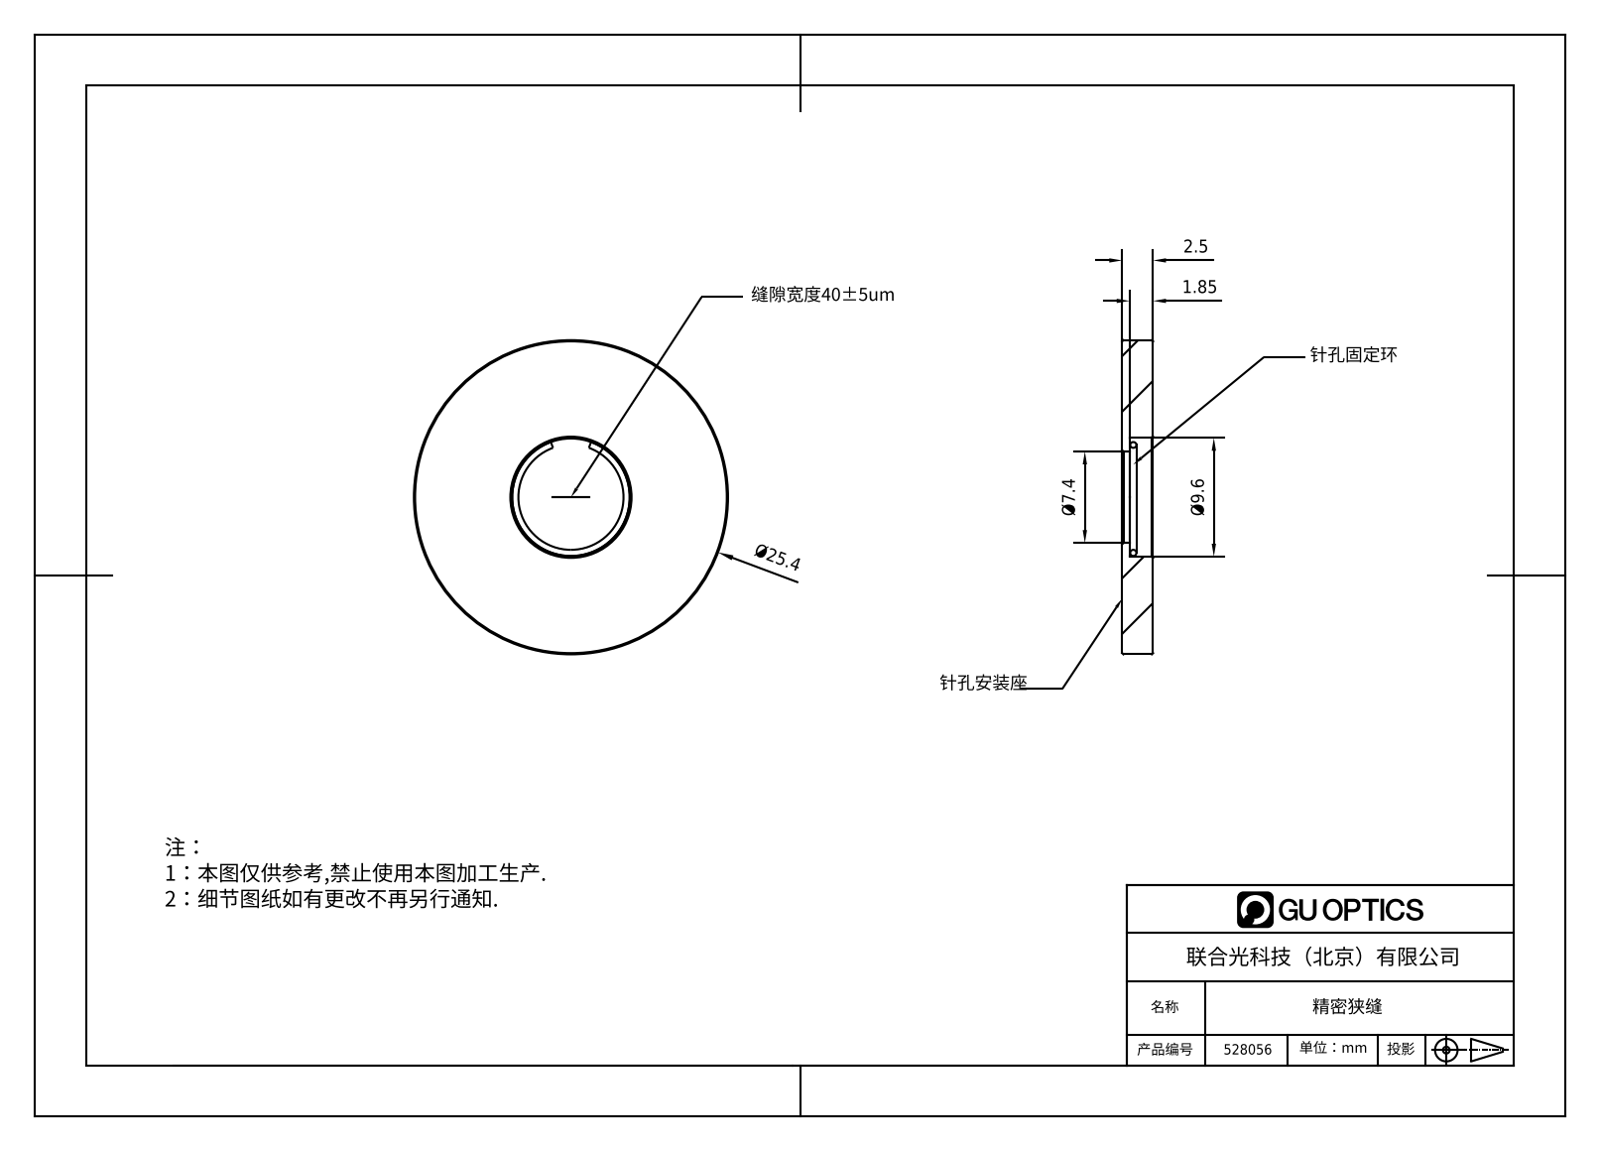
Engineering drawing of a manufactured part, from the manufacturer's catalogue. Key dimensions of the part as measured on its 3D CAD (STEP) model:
Part name (STEP PRODUCT): 528056
STEP written by: SolidWorks 2020 (CONFIG_CONTROL_DESIGN)
Units: millimetres
Bodies: 2 solids, 33 faces (11 planar, 8 cylindrical, 14 other)
Overall size (bounding box): 25.4 × 25.4 × 2.5
Volume: 1 111 mm³ · Surface area: 1 313 mm²
Round holes (diameter × count): ⌀7.4 ×1, ⌀9.6 ×1
Round bosses / shafts (diameter × count): ⌀25.4 ×1, ⌀9.5 ×1
Main face-to-face distances: 2.5, 0.65, 1.85, 0.6, 1.9, 3
